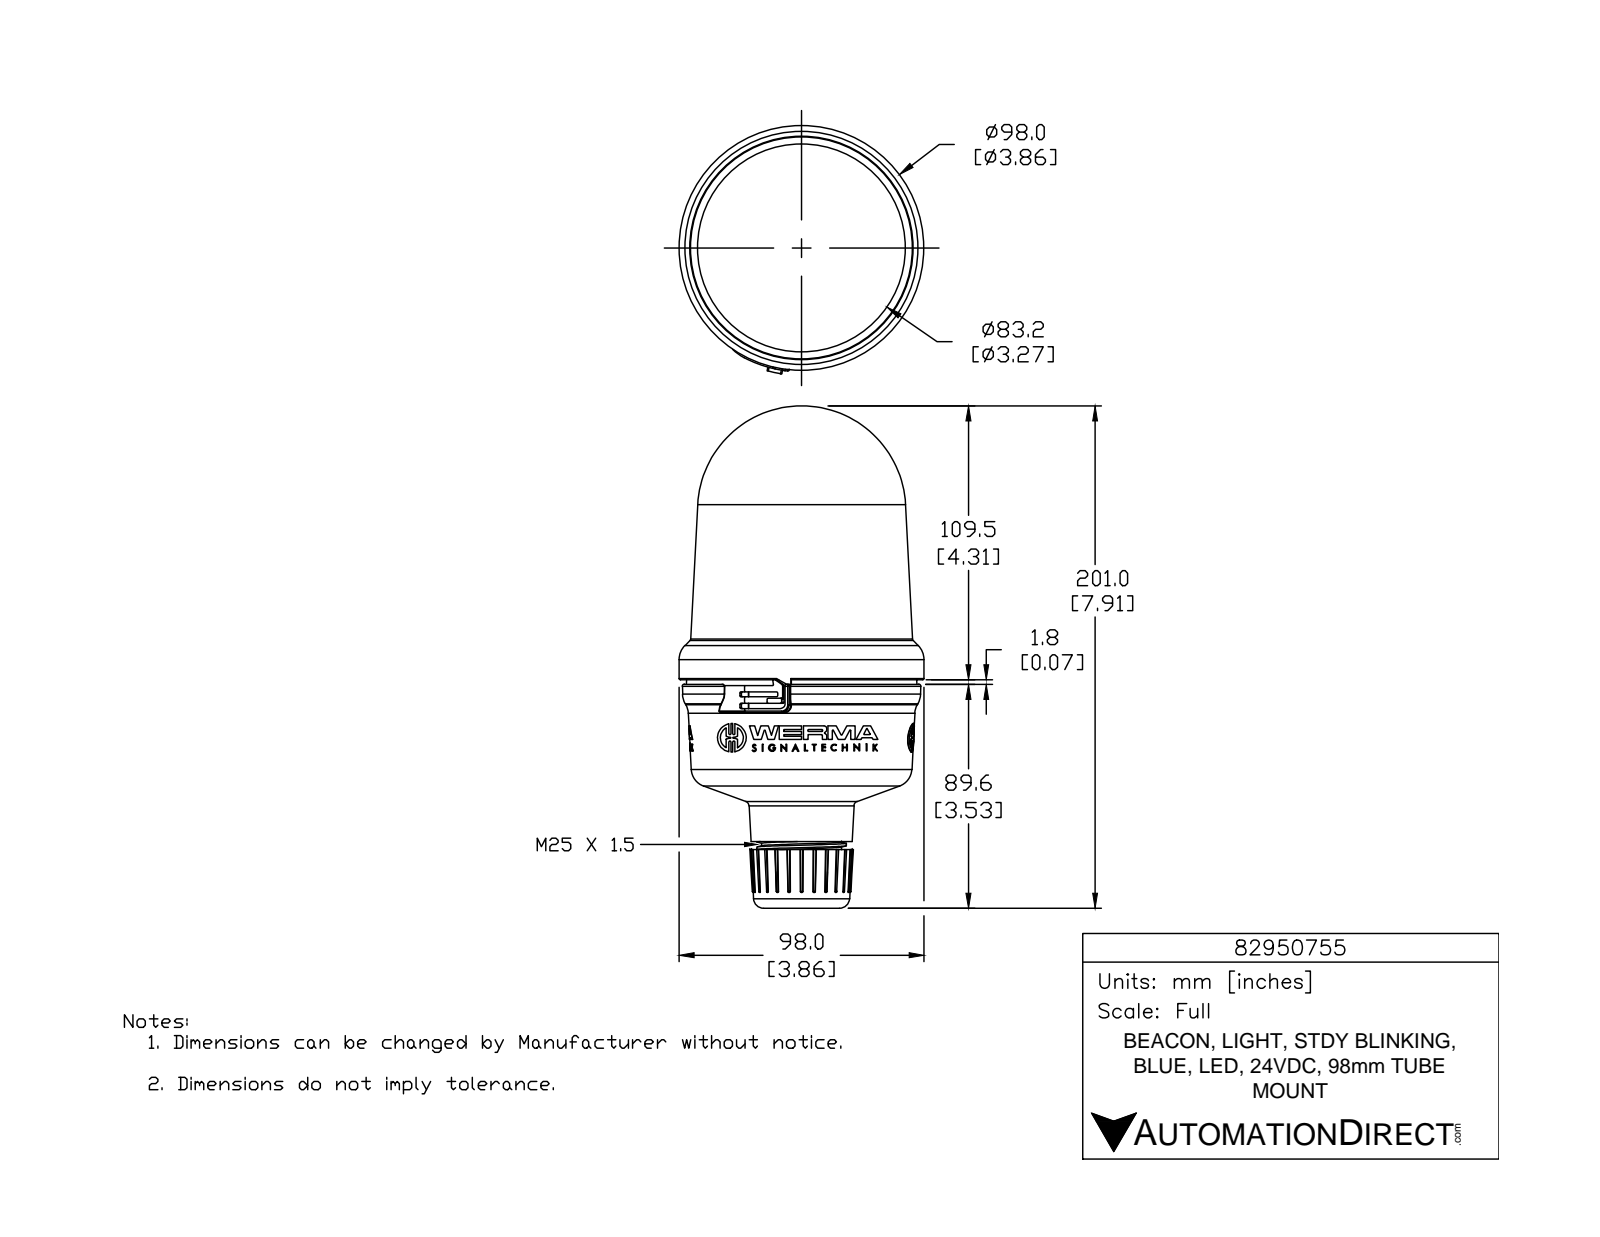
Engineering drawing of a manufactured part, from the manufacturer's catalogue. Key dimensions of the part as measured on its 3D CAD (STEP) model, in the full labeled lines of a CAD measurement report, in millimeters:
Part name (STEP PRODUCT): 82950755
STEP written by: SolidWorks 2015 (AUTOMOTIVE_DESIGN)
Units: millimetres
Bodies: 1 solid, 1006 faces (554 planar, 189 cylindrical, 263 other)
Overall size (bounding box): 201 × 99.4 × 98
Volume: 896 400 mm³ · Surface area: 58 960 mm²
Round holes (diameter × count): ⌀2 ×3, ⌀25.7 ×1, ⌀26 ×1
Round bosses / shafts (diameter × count): ⌀11.5 ×3, ⌀2.9 ×3, ⌀98 ×1, ⌀35.8 ×1, ⌀32 ×1
Partial cylindrical surfaces — rounded edges, fillets, slot ends (radius × count): R0.5 ×12, R0.2 ×9, R0.2 ×6, R0.4 ×6, R0.4 ×6, R0.4 ×6, R6.7 ×6, R0.2 ×3
Main face-to-face distances: 56.2, 11.7, 68, 8.5, 3.2, 64.7, 66.1, 62.9, 54.4, 1.9
